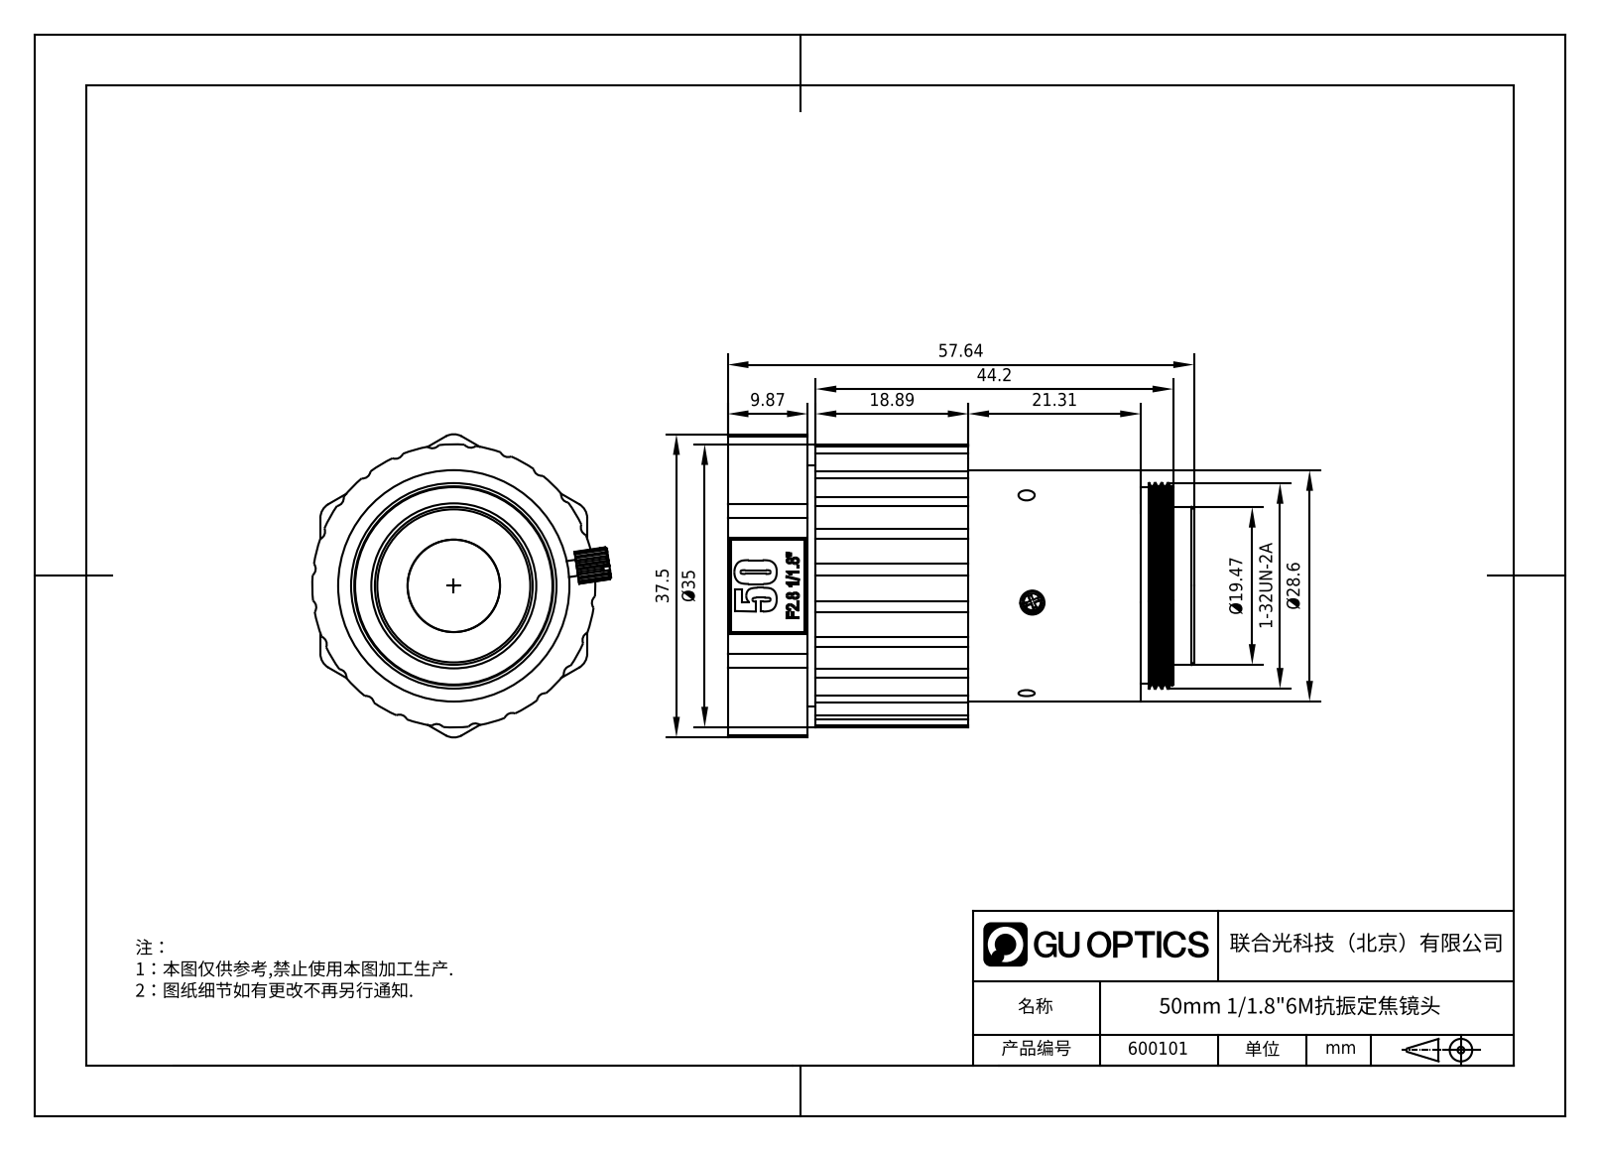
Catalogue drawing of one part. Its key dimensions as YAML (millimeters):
part_name: "600101"
step_written_by: "SolidWorks 2020 (CONFIG_CONTROL_DESIGN)"
units: millimeters
bodies: {solids: 4, faces: 406, planar: 190, cylindrical: 106, other: 110}
overall_size: [57.64, 37.49, 36.95]
volume: 34215
surface_area: 18640
round_holes:
  - {diameter: 2, count: 3}
  - {diameter: 1.4, count: 1}
  - {diameter: 3, count: 1}
  - {diameter: 20.4, count: 1}
  - {diameter: 21.6, count: 1}
  - {diameter: 30, count: 1}
  - {diameter: 31.2, count: 1}
  - {diameter: 31.4, count: 1}
round_bosses_or_shafts:
  - {diameter: 31, count: 1}
  - {diameter: 29.8, count: 1}
  - {diameter: 28.6, count: 1}
  - {diameter: 28, count: 1}
  - {diameter: 25.4, count: 1}
  - {diameter: 24.54, count: 1}
  - {diameter: 24.3, count: 1}
  - {diameter: 22, count: 1}
partial_cylinders:
  - {radius: 1, count: 24}
  - {radius: 2, count: 7}
  - {radius: 17.5, count: 1}
face_to_face_distances: [18.89, 33, 1, 29.76, 9.87, 19.89, 21.75, 25.05, 15.18, 4.71]
hole_center_spacings: [0.71]
